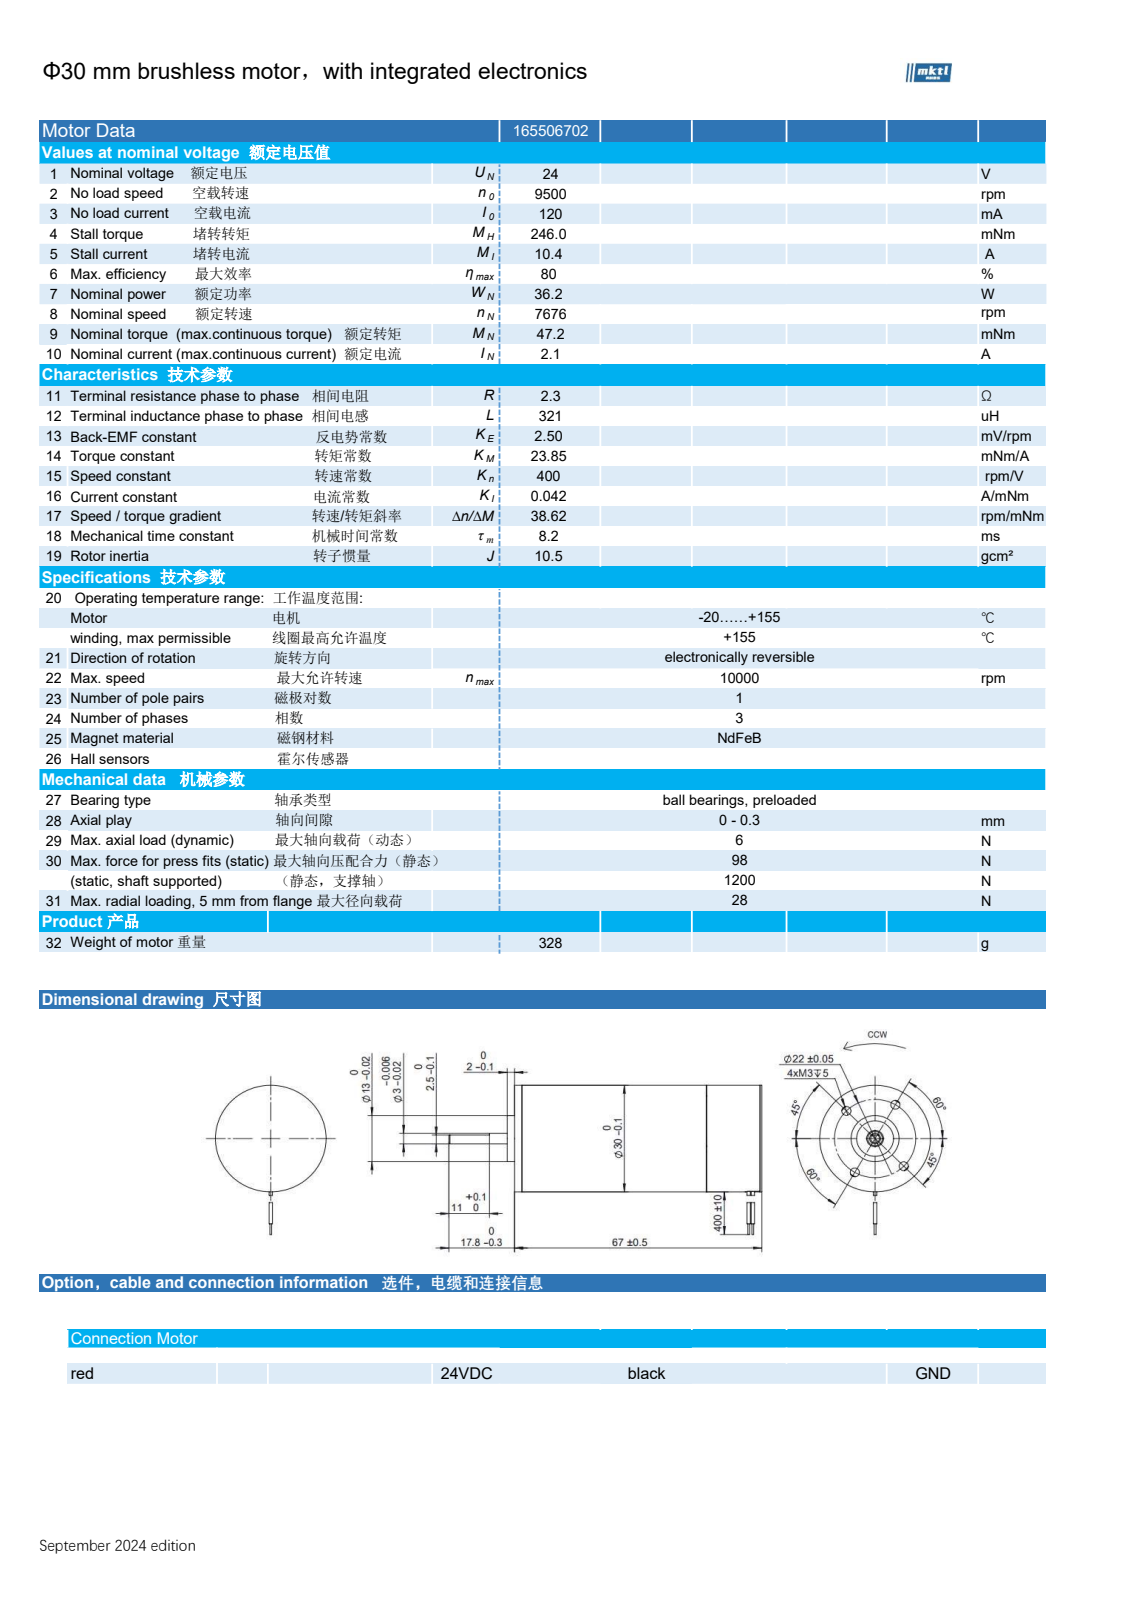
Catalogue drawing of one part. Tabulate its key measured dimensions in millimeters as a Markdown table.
| quantity | value |
| --- | --- |
| part name | approval 165506703 |
| STEP written by | SolidWorks 2018 (CONFIG_CONTROL_DESIGN) |
| units | millimeters |
| bodies | 224 solids, 2105 faces (794 planar, 1231 cylindrical, 80 other) |
| overall size | 84.8 × 42 × 30 |
| volume | 37 158 mm³ |
| surface area | 139 328 mm² |
| round holes (diameter × count) | 1.1 × 5, 1.5 × 5, 2.1 × 5, 3 × 5, 2.5 × 4, 1.2 × 3, 1.8 × 3, 1 × 2, 2 × 2, 4 × 1, 9 × 1, 10 × 1 |
| round bosses / shafts (diameter × count) | 1 × 15, 0.8 × 10, 4 × 5, 1.6 × 5, 0.9 × 3, 0.3 × 3, 0.5 × 2, 30 × 1 |
| partial cylindrical surfaces (radius × count) | 0.1 × 24, 0.75 × 6, 0.5 × 4, 1 × 2, 1.5 × 2, 8 × 2, 10.5 × 1, 12.15 × 1 |
| main face-to-face distances | 0.4, 0.6, 0.8, 1, 1.2, 1.4, 1.6, 1.8, 2, 20.5 |
| hole center spacings | 11.5, 2, 11, 11.26, 12.9, 20.79, 4, 8.62 |
